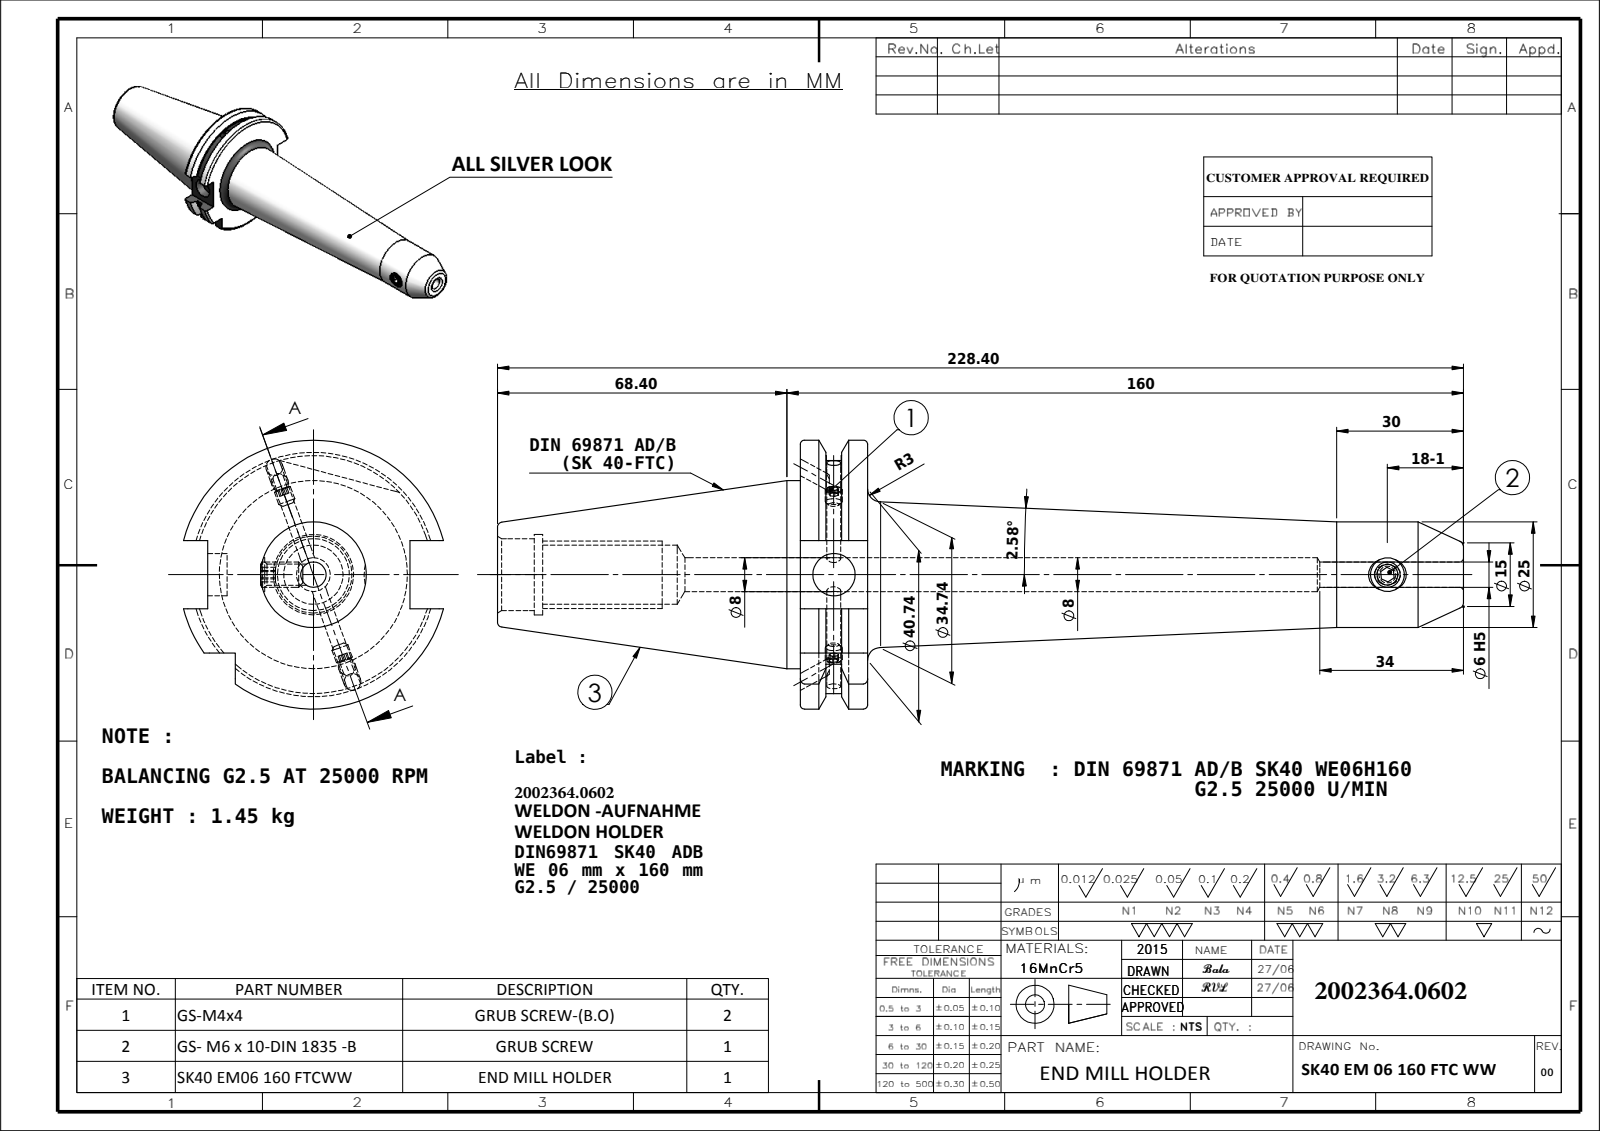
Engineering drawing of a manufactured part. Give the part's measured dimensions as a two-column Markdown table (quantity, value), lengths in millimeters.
| quantity | value |
| --- | --- |
| part name | SK40 EM06 100 FTCWW; M6X10_DIN 913 - M6 x 10-N; Copy of M4X4_DIN 913 - M4 x 4-N; 91406-WE706160 |
| STEP written by | SolidWorks 2009 (CONFIG_CONTROL_DESIGN) |
| units | millimeters |
| bodies | 4 solids, 156 faces (56 planar, 42 cylindrical, 58 other) |
| overall size | 228.4 × 63.55 × 61.48 |
| volume | 188 095 mm³ |
| surface area | 36 310 mm² |
| round holes (diameter × count) | 8 × 2, 3.3 × 1, 5 × 1, 6 × 1, 10 × 1, 14 × 1, 17 × 1, 19 × 1 |
| round bosses / shafts (diameter × count) | 4 × 2, 44.45 × 1, 25 × 1, 6 × 1 |
| partial cylindrical surfaces (radius × count) | 28.12 × 1, 31.77 × 1 |
| main face-to-face distances | 15.9, 16.1, 47.8, 71.6, 87.5, 10.7, 60.9, 76.8, 77.63, 66.93 |
| hole center spacings | 130.85 |
